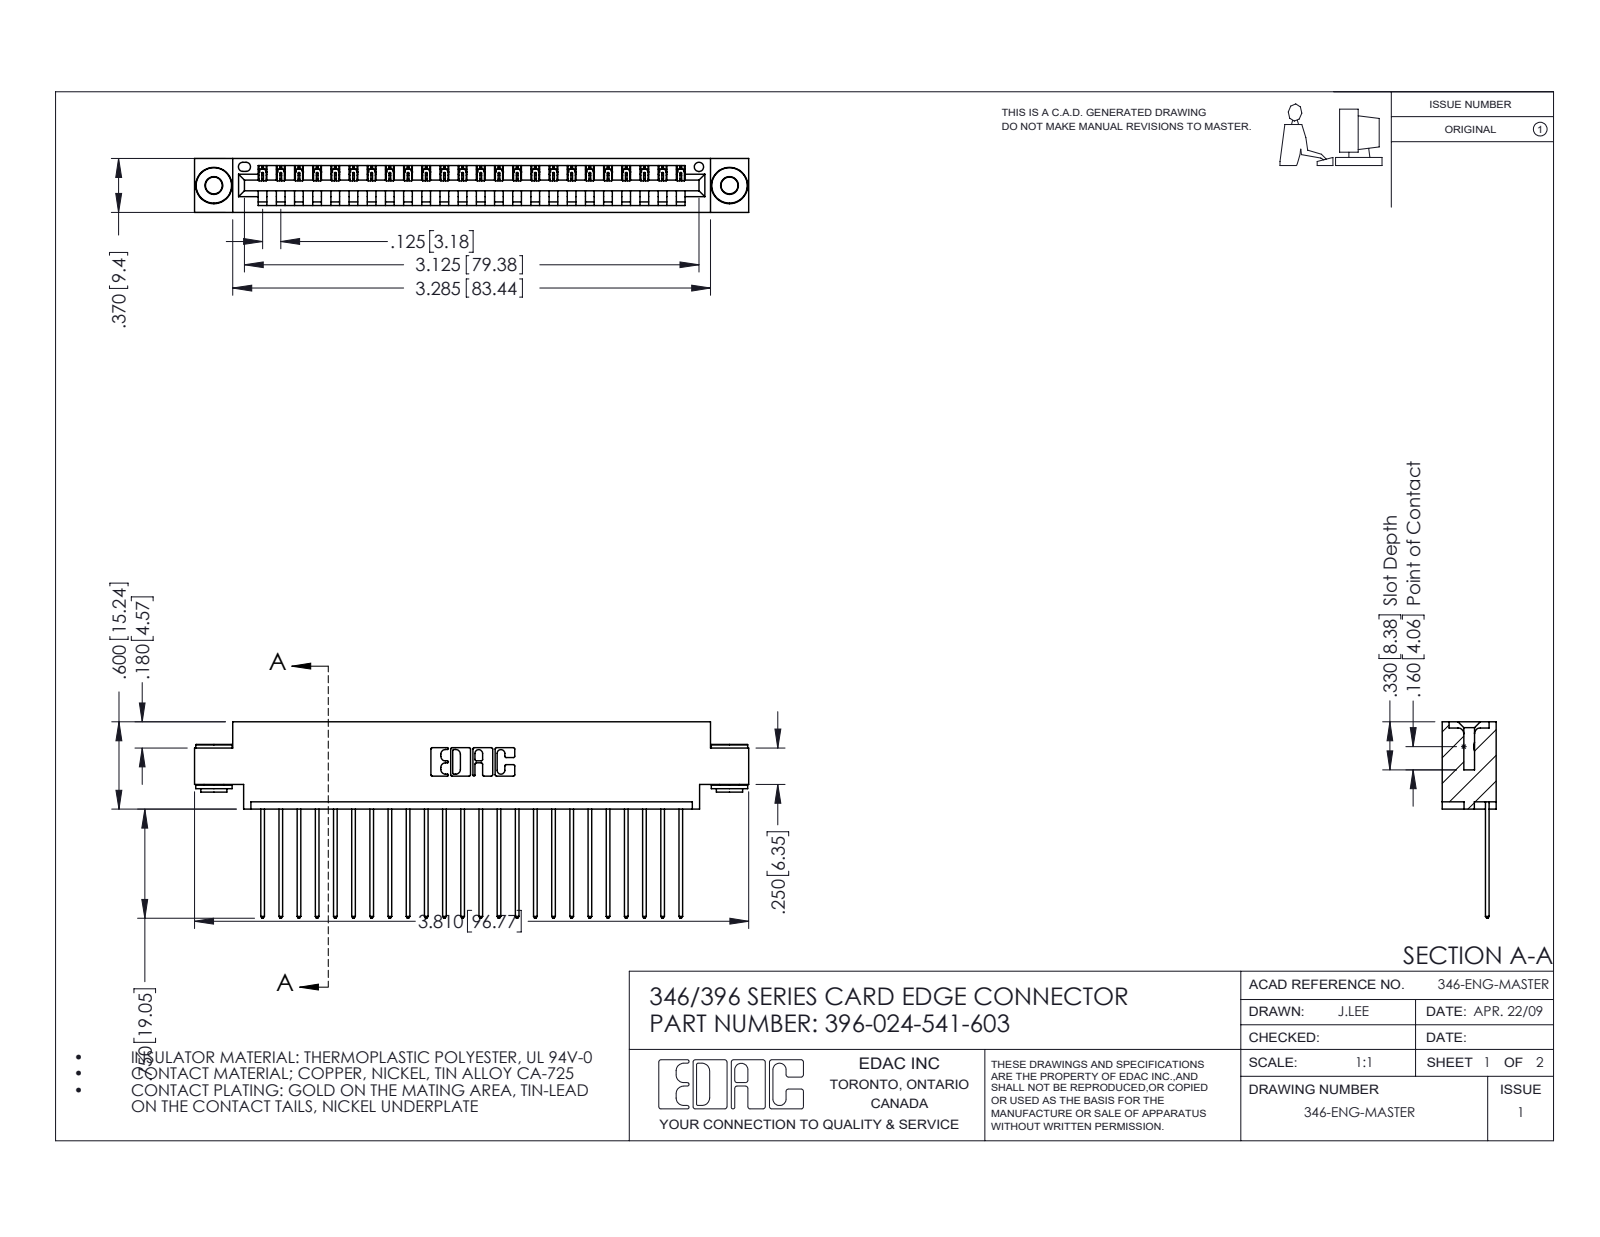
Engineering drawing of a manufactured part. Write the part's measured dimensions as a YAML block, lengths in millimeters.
part_name: "346 Part_0.170 Offset - 0.156 Dia-TH; 345-250-002_345-250-002-102; 345-292-001_345-293-141; 396-024-541-603"
step_written_by: "SolidWorks 2016 (CONFIG_CONTROL_DESIGN)"
units: millimeters
bodies: {solids: 27, faces: 1556, planar: 1050, cylindrical: 498, other: 8}
overall_size: [96.8, 34.3, 9.4]
volume: 9080
surface_area: 12010
round_holes:
  - {diameter: 2.9, count: 2}
  - {diameter: 4, count: 2}
  - {diameter: 1.6, count: 1}
round_bosses_or_shafts:
  - {diameter: 6.4, count: 2}
  - {diameter: 4.6, count: 2}
  - {diameter: 3.5, count: 2}
partial_cylinders:
  - {radius: 0.2, count: 48}
  - {radius: 0.3, count: 48}
  - {radius: 0.3, count: 22}
  - {radius: 0.2, count: 6}
  - {radius: 0.8, count: 6}
  - {radius: 0.7, count: 3}
  - {radius: 0.8, count: 2}
  - {radius: 1, count: 2}
face_to_face_distances: [1.2, 8.2, 9.4, 6.4, 0.6, 1.8, 7.6, 3.8, 5.6, 2.5]
hole_center_spacings: [6.2, 84.8, 90]
